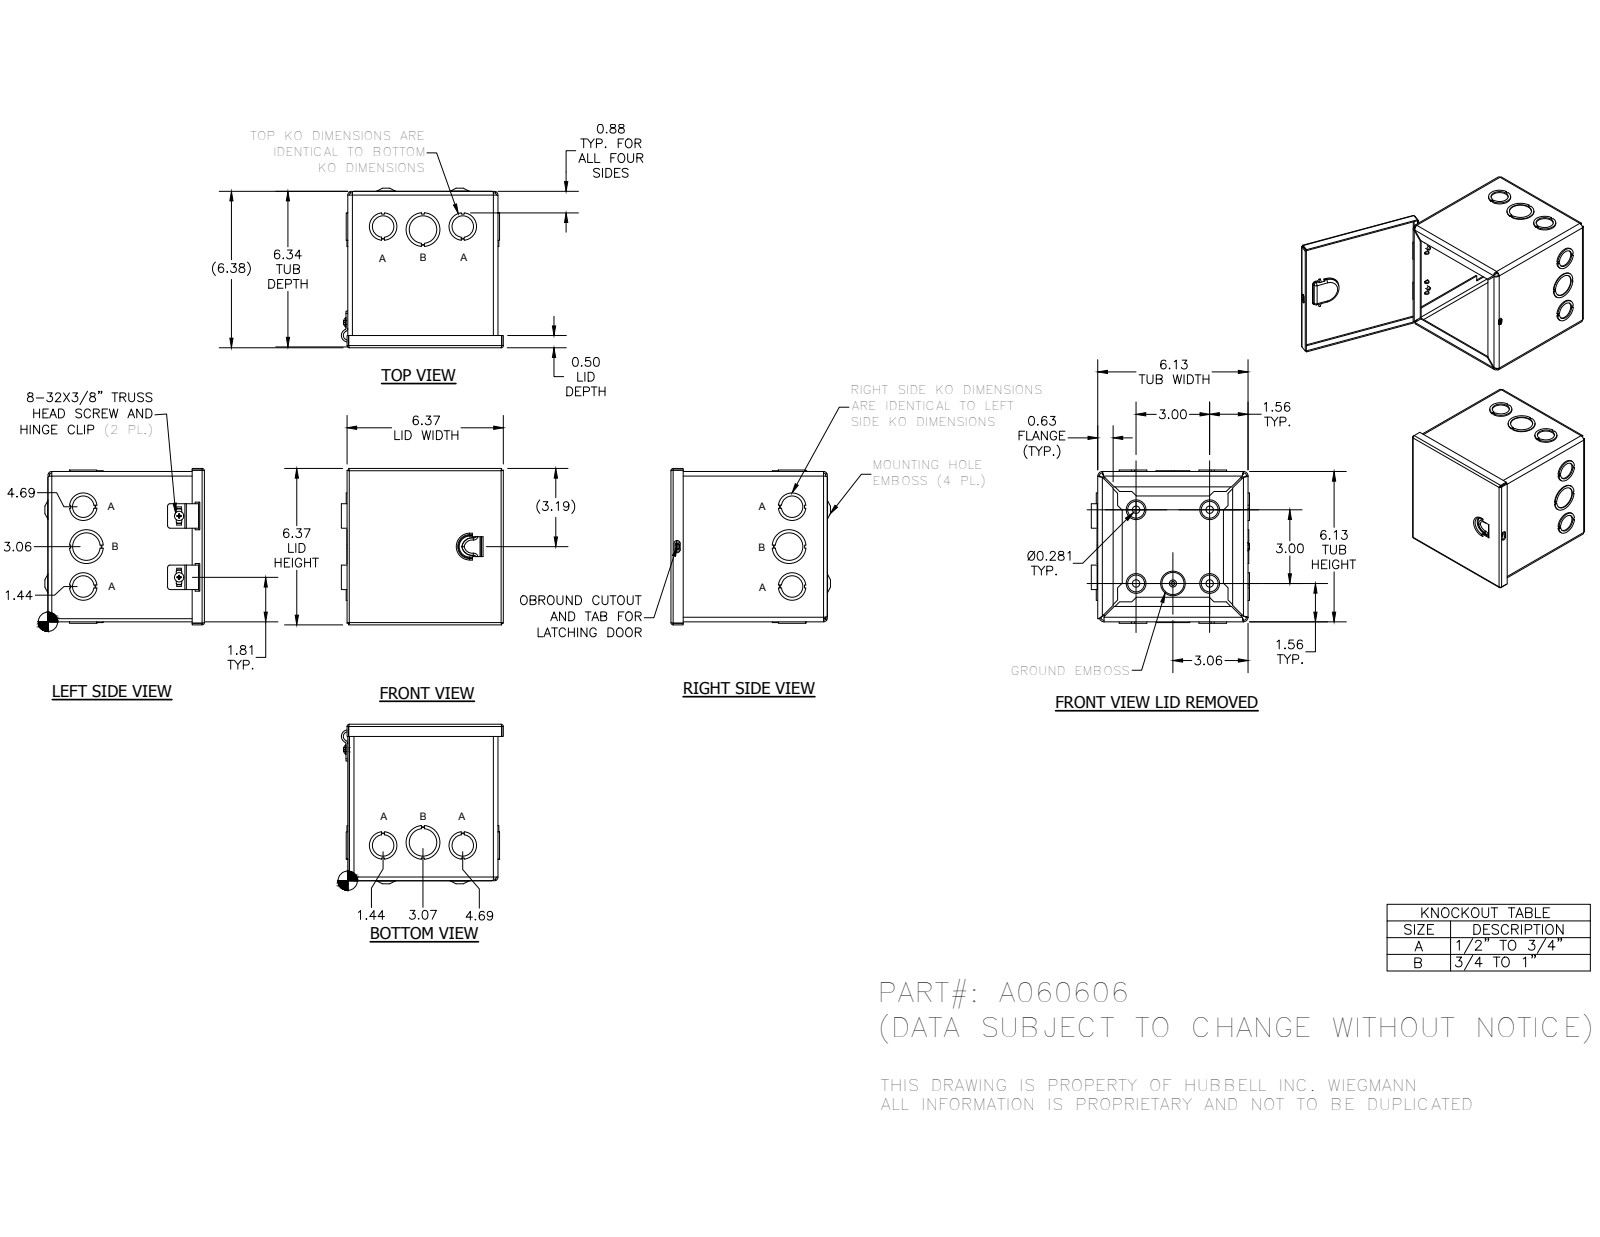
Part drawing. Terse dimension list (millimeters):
name: A0606BA; A060606WRA; 31816; 372177 (+3 more)
written by: Autodesk Inventor 2014 (AUTOMOTIVE_DESIGN)
unit: mm
bodies: 23 solids, 831 faces (494 planar, 179 cylindrical, 158 other)
size: 168.57 × 165.19 × 163.49
holes: 6× ⌀28.57, 4× ⌀7.62, 4× ⌀22.22, 2× ⌀3.56, 2× ⌀34.92, 1× ⌀4.19
bosses: 2× ⌀9.75, 2× ⌀4.17, 1× ⌀5.8
rounds: 15× R3.17, 10× R0.79, 9× R1.59, 8× R2.38, 8× R4.75, 4× R1.4, 4× R1.57, 4× R1.78
face distances: 1.58, 1.57, 155.58, 154, 152.43, 154.01, 160.43, 158.85, 1.59, 160.44
hole spacings: 76.2, 38.1, 41.39, 41.4, 82.55, 85.19, 99.66, 101.14
